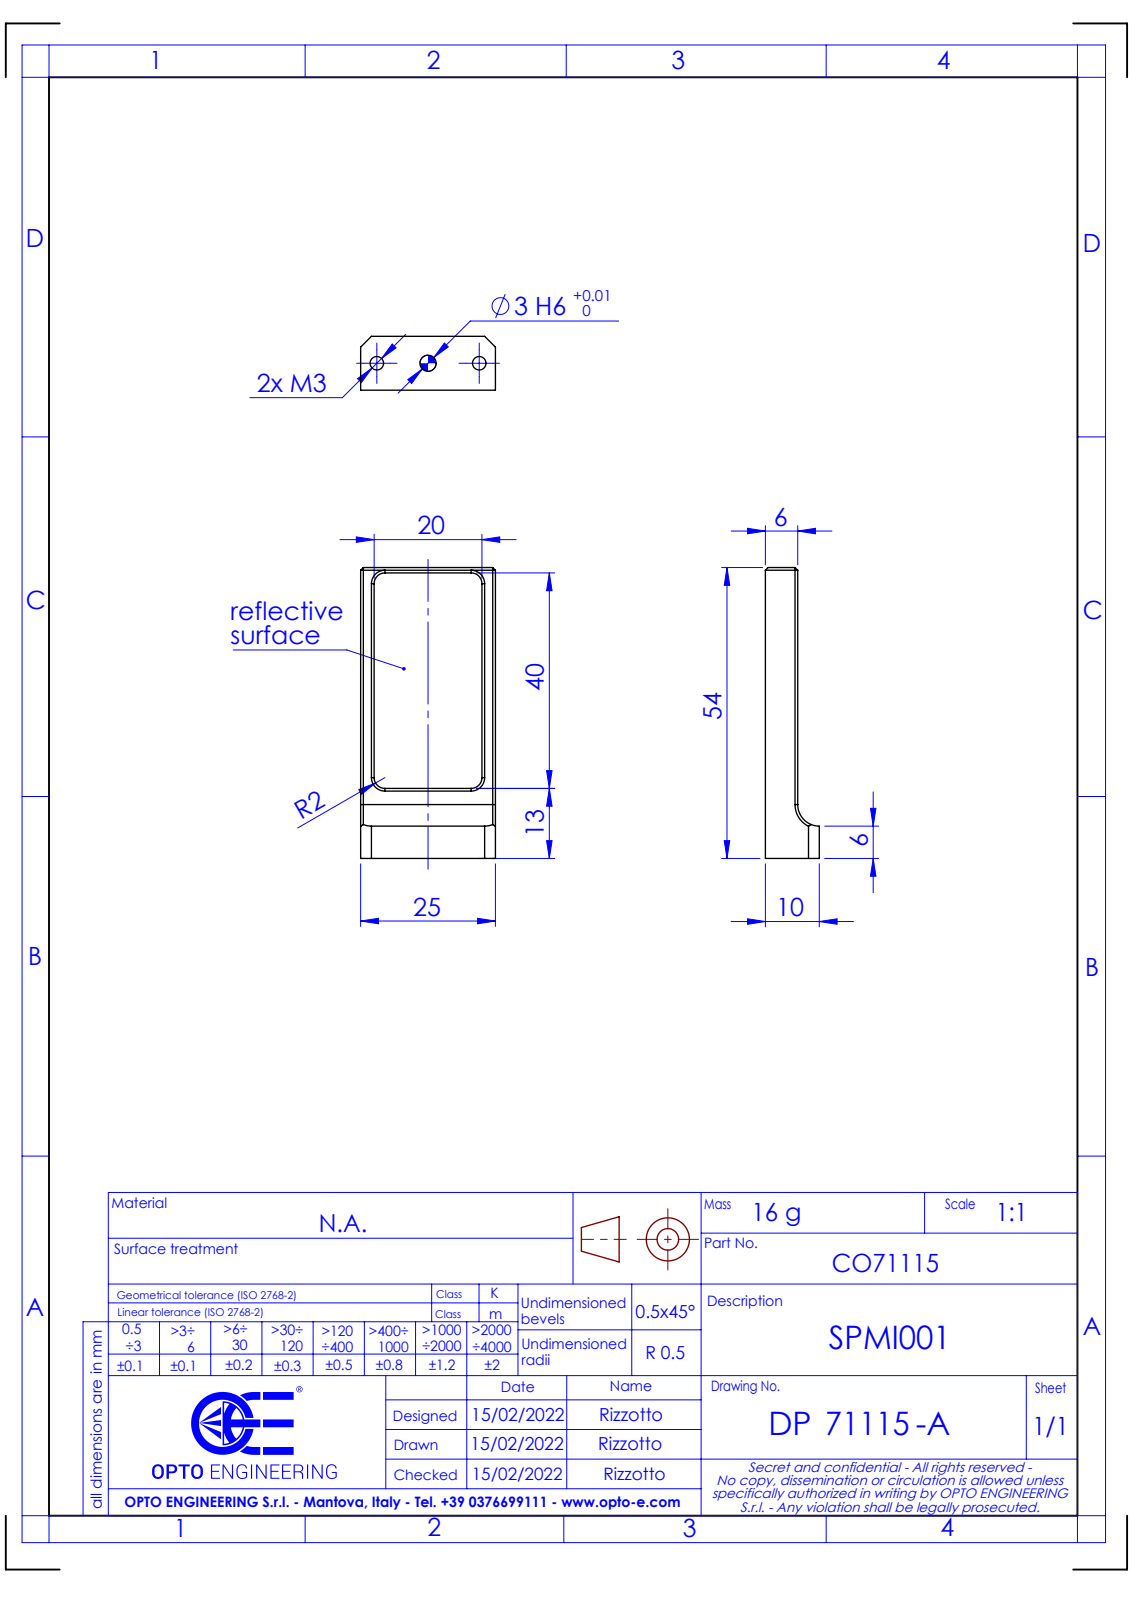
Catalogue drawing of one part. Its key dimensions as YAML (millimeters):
part_name: "DP71115-A_SPMI001"
step_written_by: "SolidWorks 2021 (CONFIG_CONTROL_DESIGN)"
units: millimeters
bodies: {solids: 0, faces: 56, planar: 30, cylindrical: 20, other: 6}
overall_size: [54, 25, 10]
round_holes:
  - {diameter: 2.5, count: 2}
  - {diameter: 3, count: 1}
partial_cylinders:
  - {radius: 1, count: 8}
  - {radius: 2, count: 4}
  - {radius: 4, count: 1}
face_to_face_distances: [3, 5, 2, 1.5, 23.5, 1, 4, 25, 22, 6]
hole_center_spacings: [9.5, 19]
